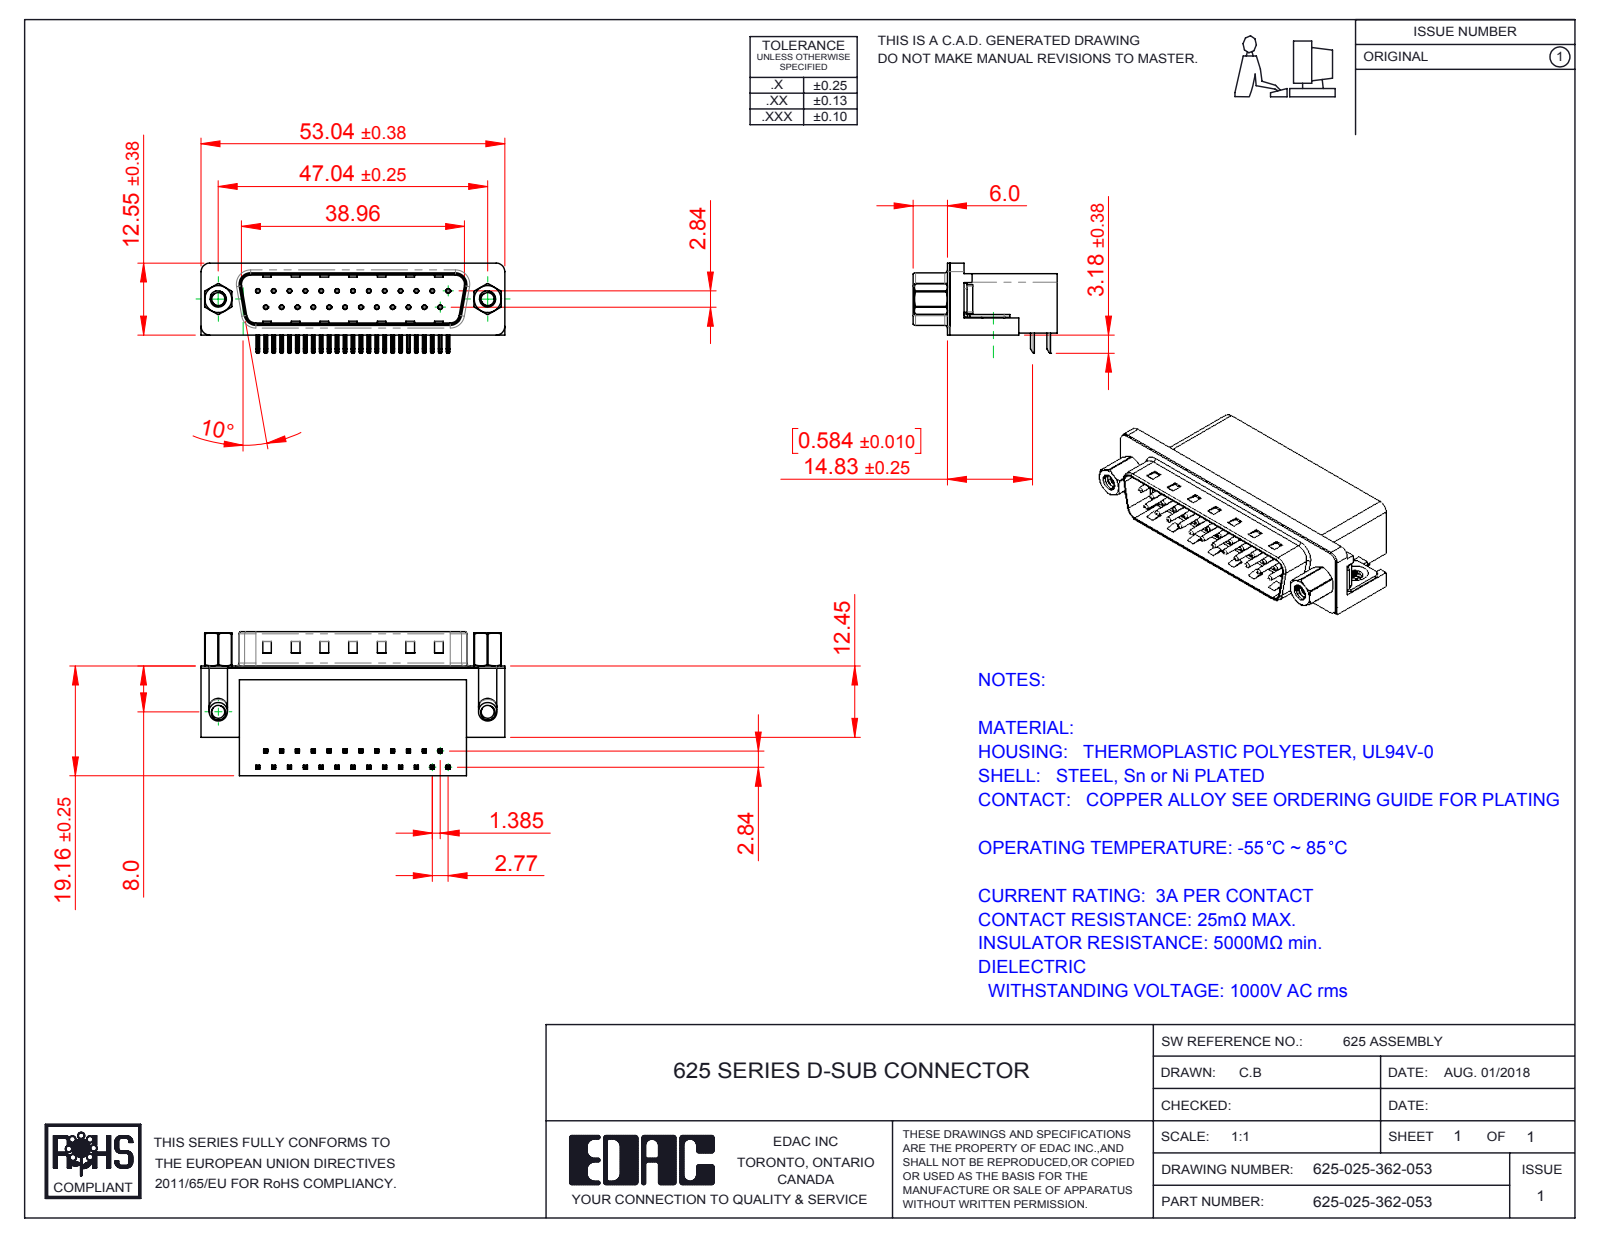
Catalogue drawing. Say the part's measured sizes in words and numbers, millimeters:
The part is named "625 Contact Top; 625 Housing_25 Socket; 625 Contact Bottom; 625 Shell_25 Socket (+4 more)". Its 3-D file was written by "SolidWorks 2016 (CONFIG_CONTROL_DESIGN)". It is 33 solids with 2423 faces: 1429 planar, 745 cylindrical and 249 other. Overall it measures 53.04 by 25.16 by 15.73 millimeters. Its volume is 9 389 cubic millimeters and its surface area 9 424 square millimeters. Round holes: 25 of diameter 0.35, 25 of diameter 0.8, 4 of diameter 2.26, 2 of diameter 2.29, 2 of diameter 4, 2 of diameter 4.8, 2 of diameter 5. Round bosses or shafts: 25 of diameter 0.75, 2 of diameter 4.9, 2 of diameter 4.75, 2 of diameter 3.9, 2 of diameter 3.26, 2 of diameter 2.79. Partial cylindrical surfaces (rounded edges, fillets, slot ends): 108 of radius 0.25, 50 of radius 0.12, 16 of radius 1, 9 of radius 0.5, 8 of radius 1.6, 7 of radius 1.5, 4 of radius 0.9, 4 of radius 2. The main face-to-face distances are 0.4, 10.35, 18.76, 2.1, 8.76, 10.46, 10.86, 1.7, 19.16, 10.11. The hole center spacings are 3.16, 2.77, 11.08, 5.54, 8.31, 5.03, 13.85, 7.48.
